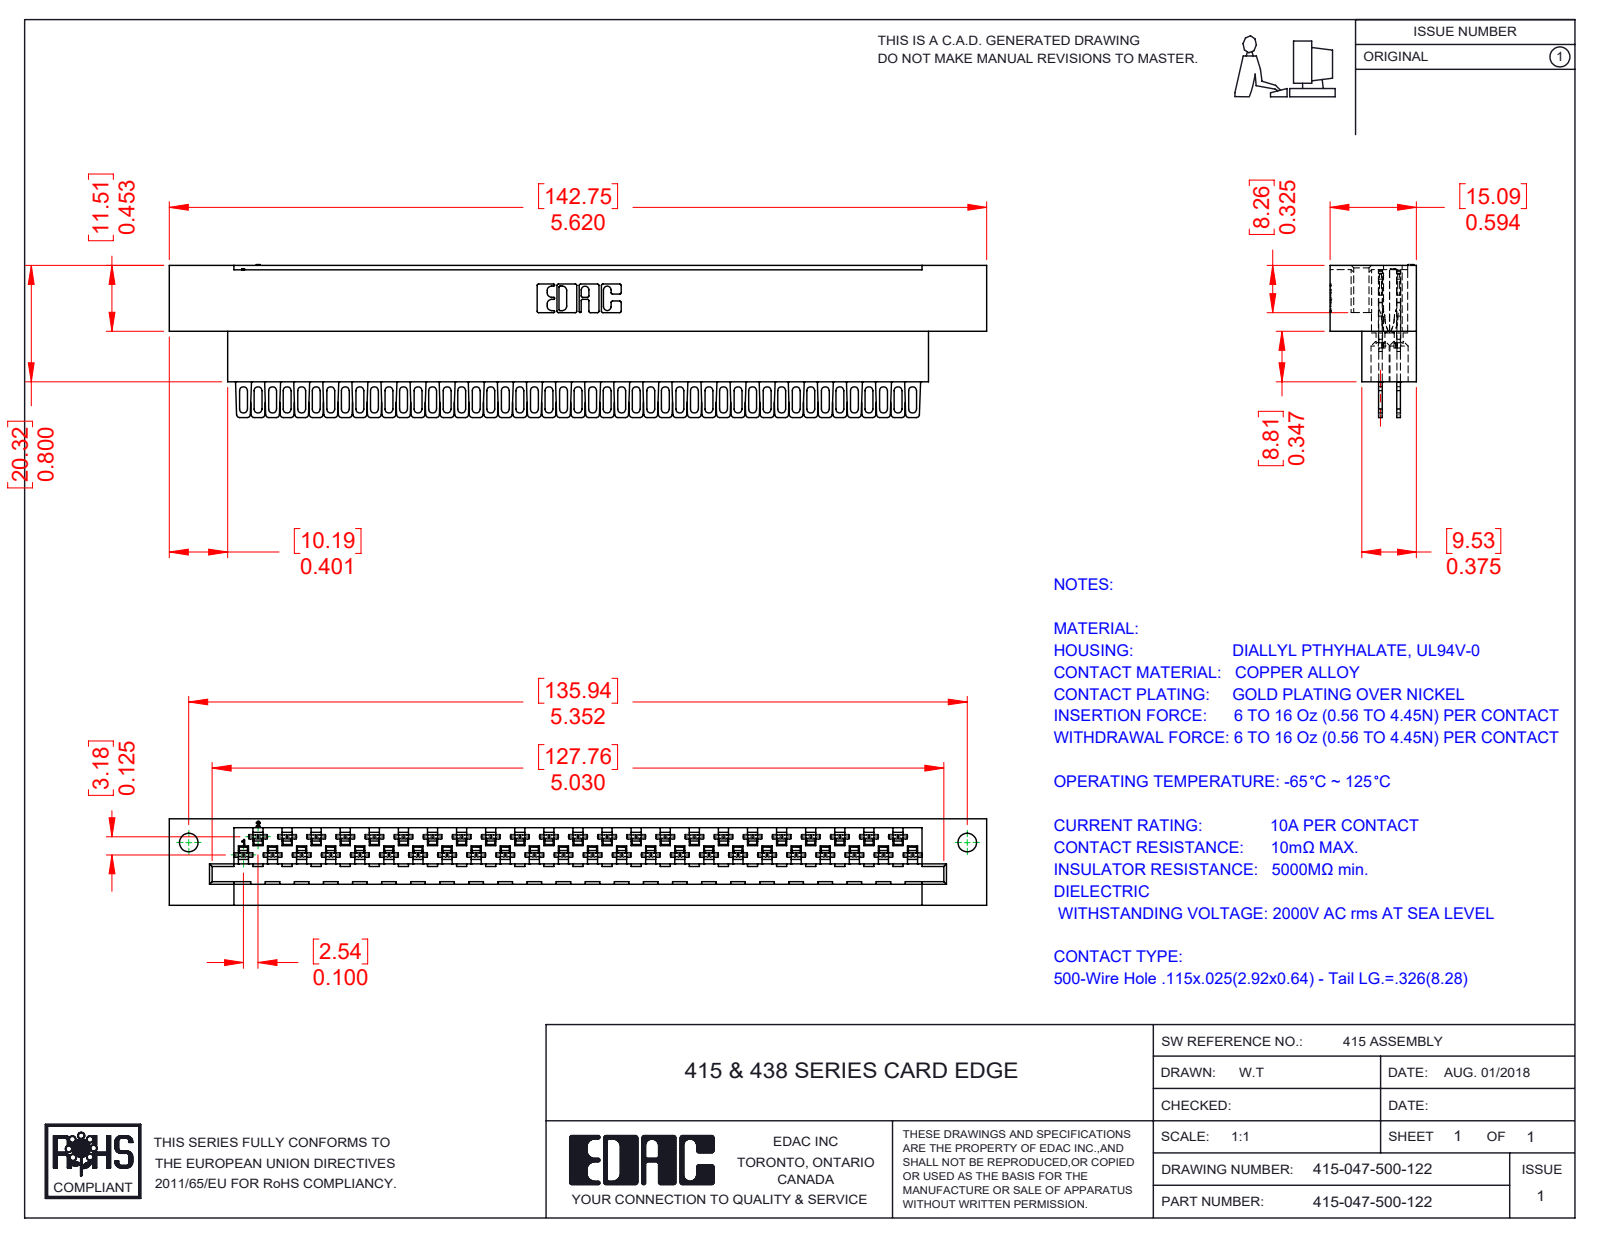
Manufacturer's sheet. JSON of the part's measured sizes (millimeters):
{"part_name": "415-047-500-122; 516-290-001_500; 415-210-001_415-210-047-122", "step_written_by": "SolidWorks 2016 (CONFIG_CONTROL_DESIGN)", "units": "millimeters", "bodies": {"solids": 48, "faces": 4938, "planar": 3086, "cylindrical": 1407, "other": 445}, "overall_size": [142.75, 26.68, 15.09], "volume_mm3": 25880, "surface_area_mm2": 30829, "round_holes": [[1.27, 47], [3.3, 47], [3.25, 2]], "partial_cylinders_radius": [[0.3, 188], [0.56, 188], [0.18, 94], [0.2, 94], [0.41, 94], [0.51, 94], [0.69, 94], [2.03, 94]], "face_to_face_distances": [3.18, 0.61, 1.27, 1.88, 15.09, 1.94, 0.67, 6.61, 8.48, 6], "hole_center_spacings": [5.08, 10.16, 15.24, 20.32, 25.4, 30.48, 35.56, 2.54]}
